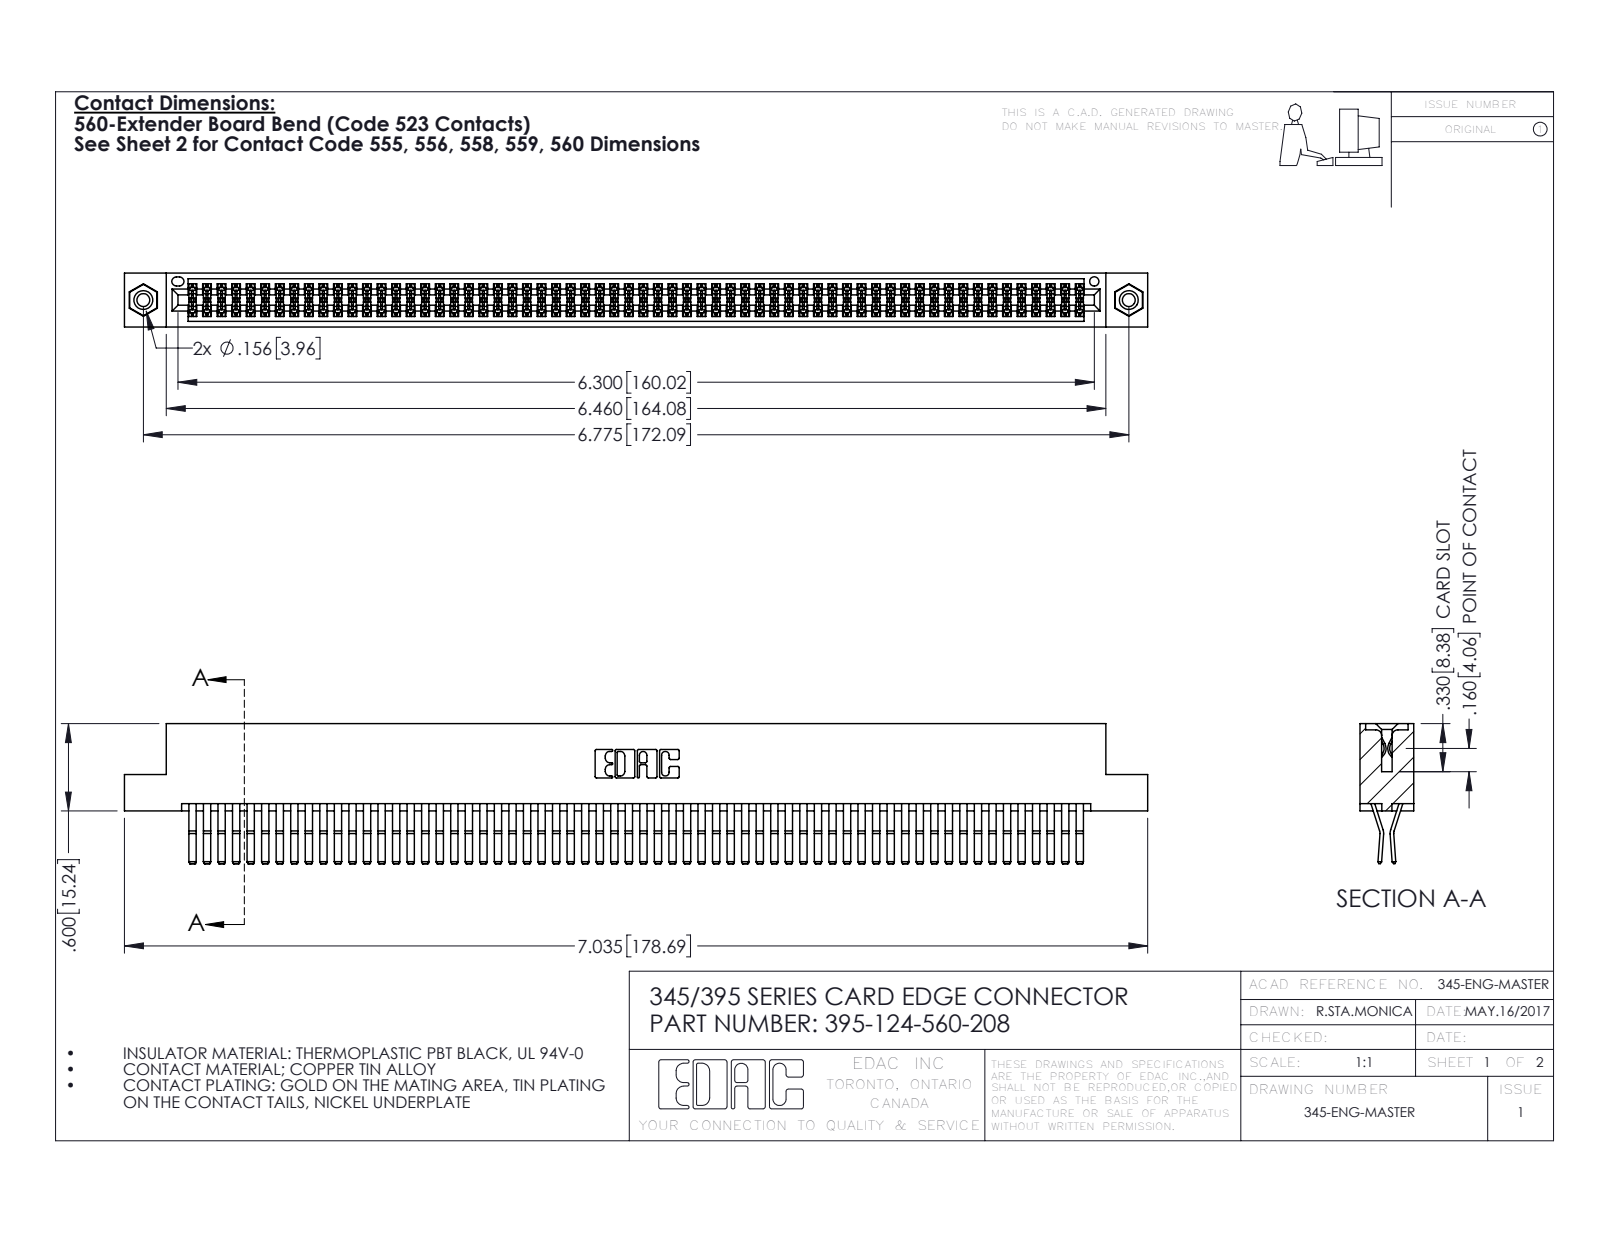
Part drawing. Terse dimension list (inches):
name: 345-250-001_345-250-003-102; 345-292-001_560 Tail; 395-124-560-208; 345 Part_Flush Mounting Lugs - 0.156 Dia-TI
written by: SolidWorks 2016 (CONFIG_CONTROL_DESIGN)
unit: in
bodies: 127 solids, 6634 faces (4204 planar, 2414 cylindrical, 16 other)
size: 7.035 × 0.962 × 0.37
volume: 1.12 in³; area: 45.9 in²
holes: 2× ⌀0.089, 2× ⌀0.125, 2× ⌀0.156, 1× ⌀0.064
bosses: 2× ⌀0.155
rounds: 187× R0.006, 22× R0.01, 6× R0.007, 6× R0.031, 3× R0.026, 2× R0.01, 2× R0.014, 2× R0.019
face distances: 0.025, 0.072, 0.298, 0.37, 0.2, 0.098, 0.272, 0.225, 0.175, 0.149
hole spacings: 0.27, 6.539, 6.775
